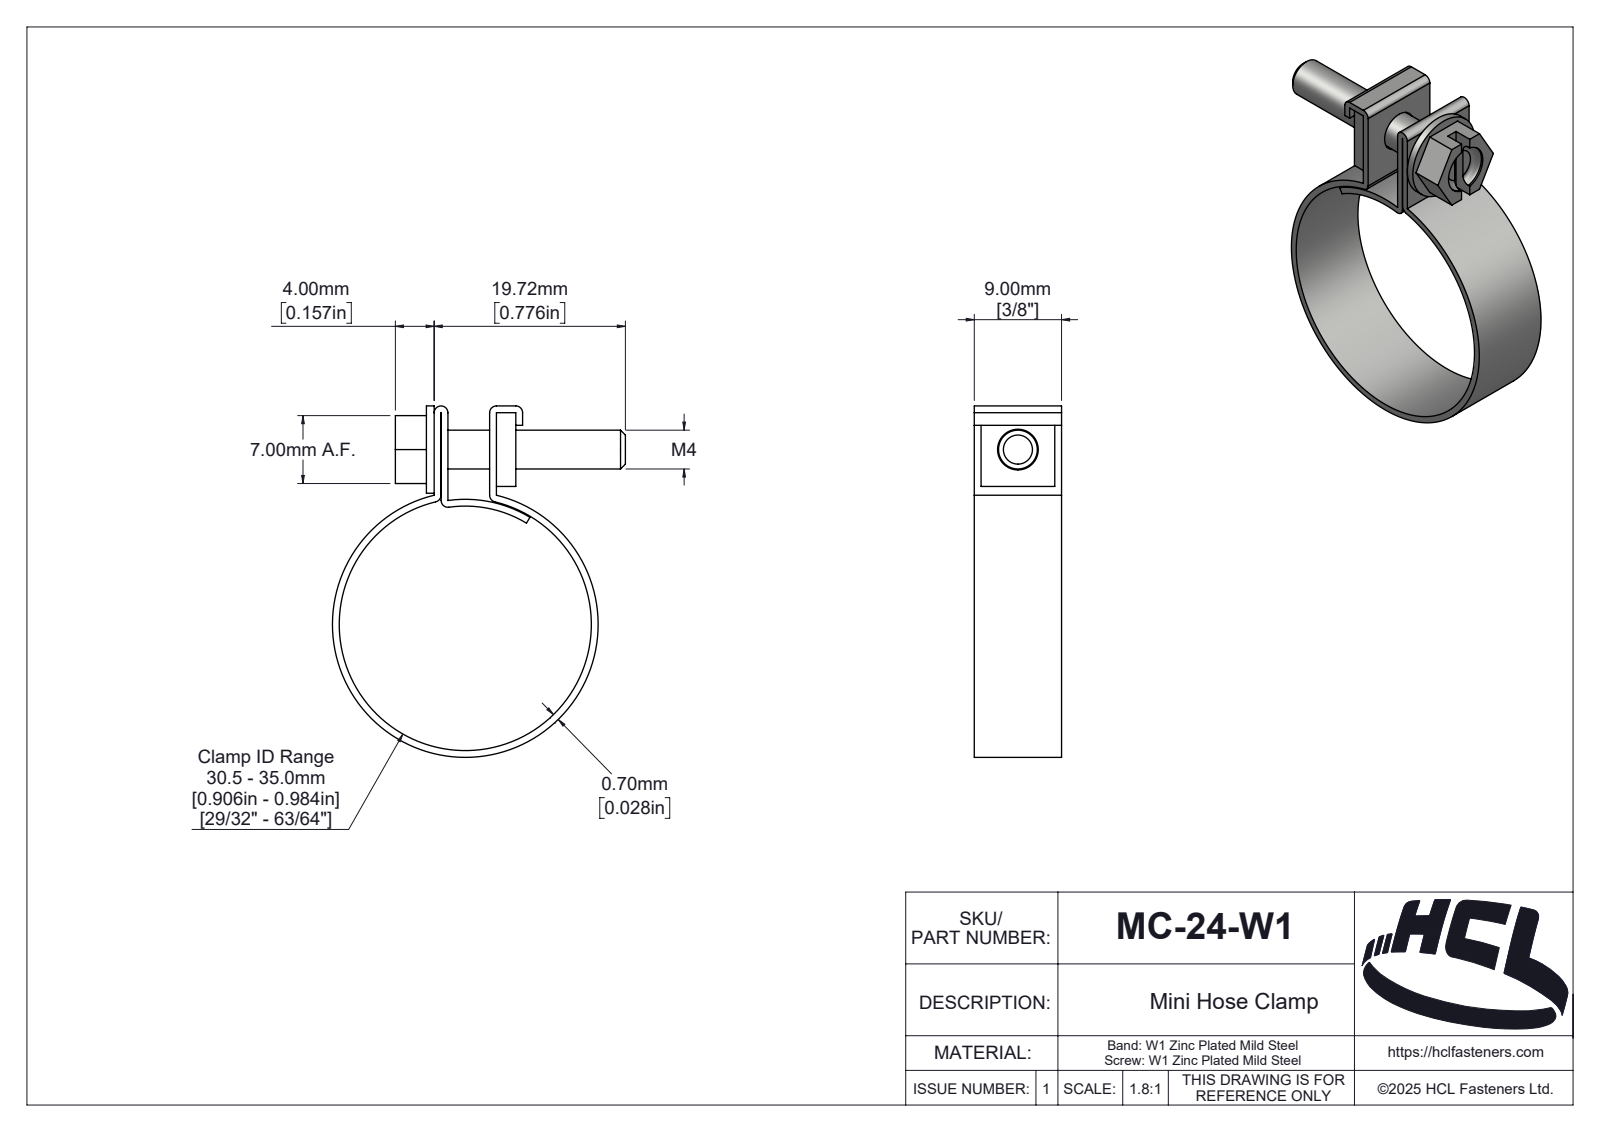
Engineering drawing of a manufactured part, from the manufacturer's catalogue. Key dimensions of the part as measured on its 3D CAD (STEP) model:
Part name (STEP PRODUCT): MC-24-W1
STEP written by: SolidWorks 2025 (AUTOMOTIVE_DESIGN)
Units: millimetres
Bodies: 3 solids, 170 faces (38 planar, 79 cylindrical, 53 other)
Overall size (bounding box): 36.22 × 30.21 × 9
Volume: 1 214 mm³ · Surface area: 2 943 mm²
Round holes (diameter × count): ⌀4.2 ×1, ⌀5 ×1, ⌀26 ×1
Round bosses / shafts (diameter × count): ⌀27.4 ×1, ⌀9 ×1, ⌀4 ×1
Partial cylindrical surfaces — rounded edges, fillets, slot ends (radius × count): R0.7 ×5, R0.2 ×1, R0.71 ×1, R0.81 ×1, R1.01 ×1, R1.06 ×1, R1.28 ×1, R1.81 ×1
Main face-to-face distances: 0.7, 5, 0.72, 5.72, 6.42, 7, 9, 2, 2.7, 8.42
